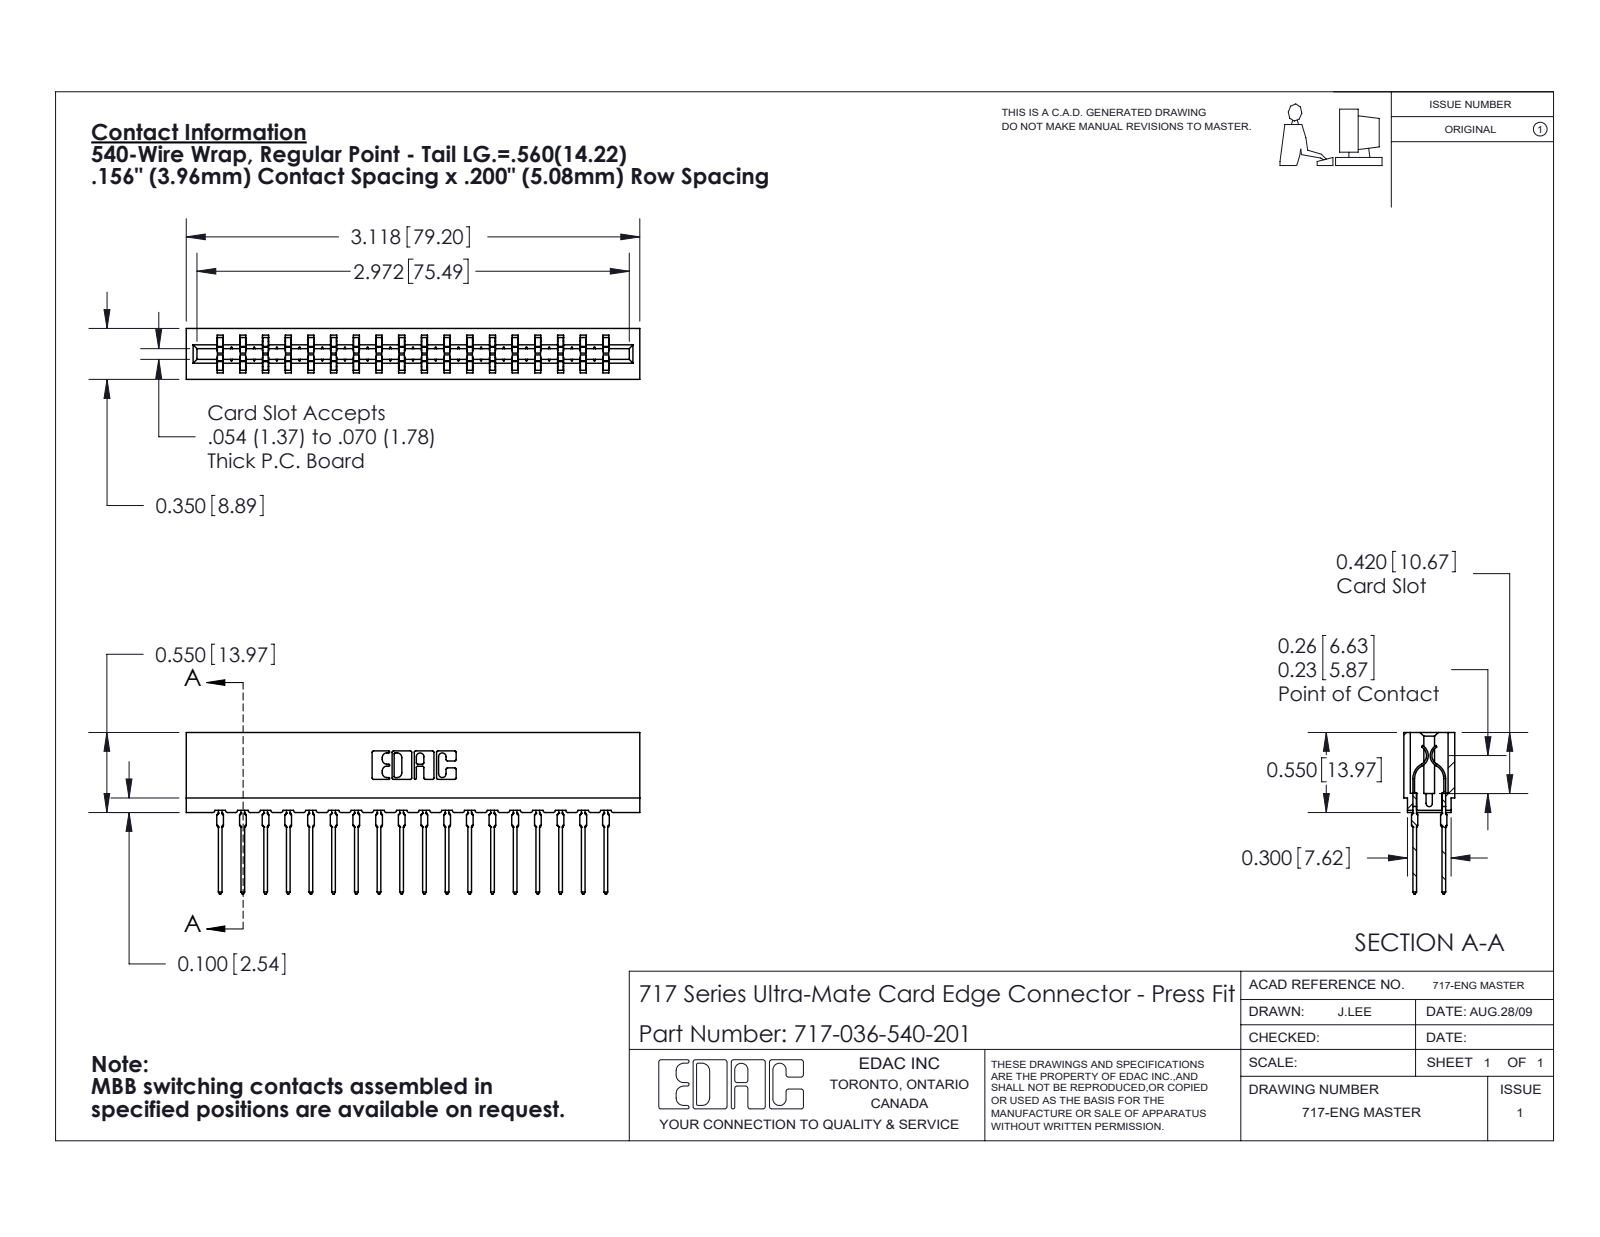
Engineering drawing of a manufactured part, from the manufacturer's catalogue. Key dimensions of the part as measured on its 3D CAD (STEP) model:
Part name (STEP PRODUCT): 717-036-540-201; 717 Part_Insulator Option - 06; 745-292-001_540
STEP written by: SolidWorks 2020 (CONFIG_CONTROL_DESIGN)
Units: inches
Bodies: 37 solids, 3334 faces (1728 planar, 670 cylindrical, 936 other)
Overall size (bounding box): 3.118 × 1.109 × 0.35
Volume: 0.431 in³ · Surface area: 16.98 in²
Partial cylindrical surfaces — rounded edges, fillets, slot ends (radius × count): R0.021 ×72, R0.015 ×36, R0.01 ×22, R0.005 ×8, R0.011 ×8, R0.007 ×6, R0.031 ×6, R0.026 ×3
Main face-to-face distances: 0.212, 0.138, 0.35, 0.156, 0.063, 0.287, 0.076, 0.149, 0.624, 0.074
